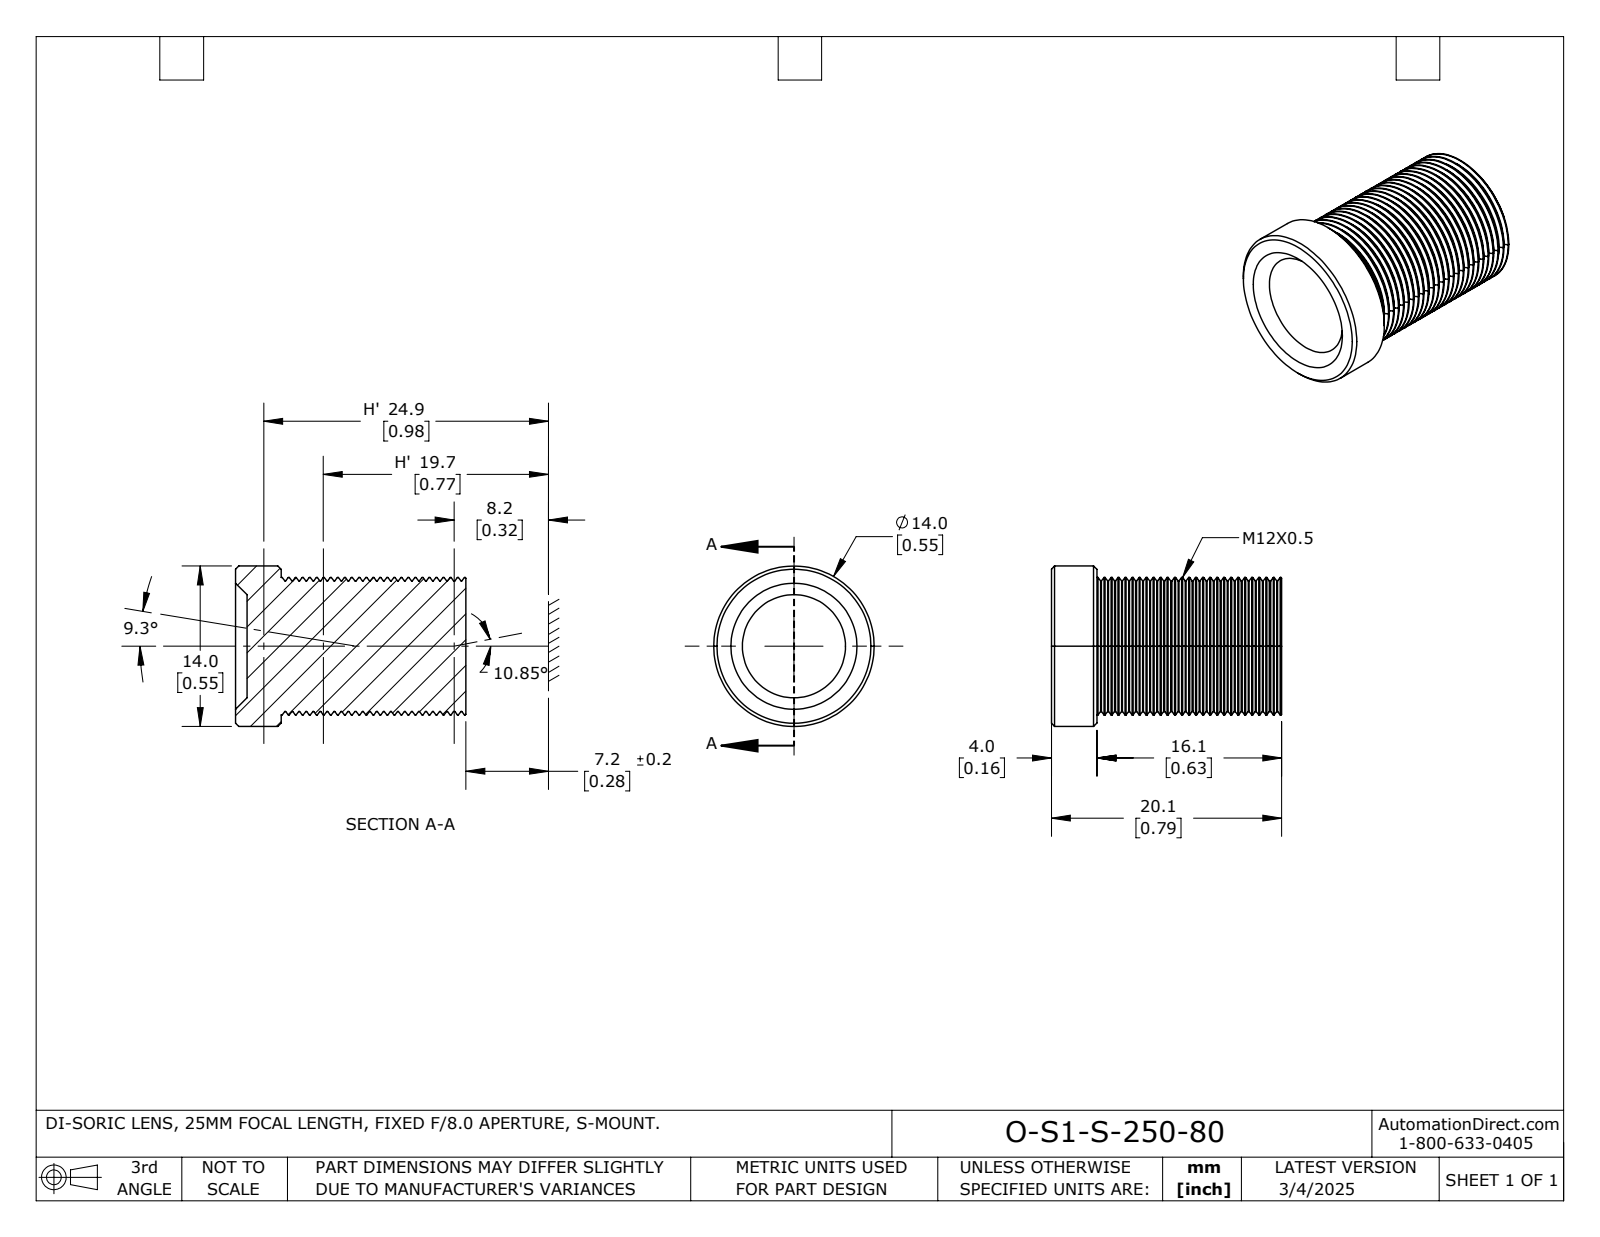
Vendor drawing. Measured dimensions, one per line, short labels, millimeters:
name: O-S1-S-250-80 -- 213101
written by: SolidWorks 2024 (AUTOMOTIVE_DESIGN)
unit: mm
bodies: 1 solid, 221 faces (3 planar, 108 cylindrical, 110 other)
size: 20.1 × 14 × 14
volume: 2 345 mm³; area: 1 346 mm²
bosses: 1× ⌀14, 1× ⌀12, 1× ⌀11.4
face distances: 20.11, 3.98, 16.13
